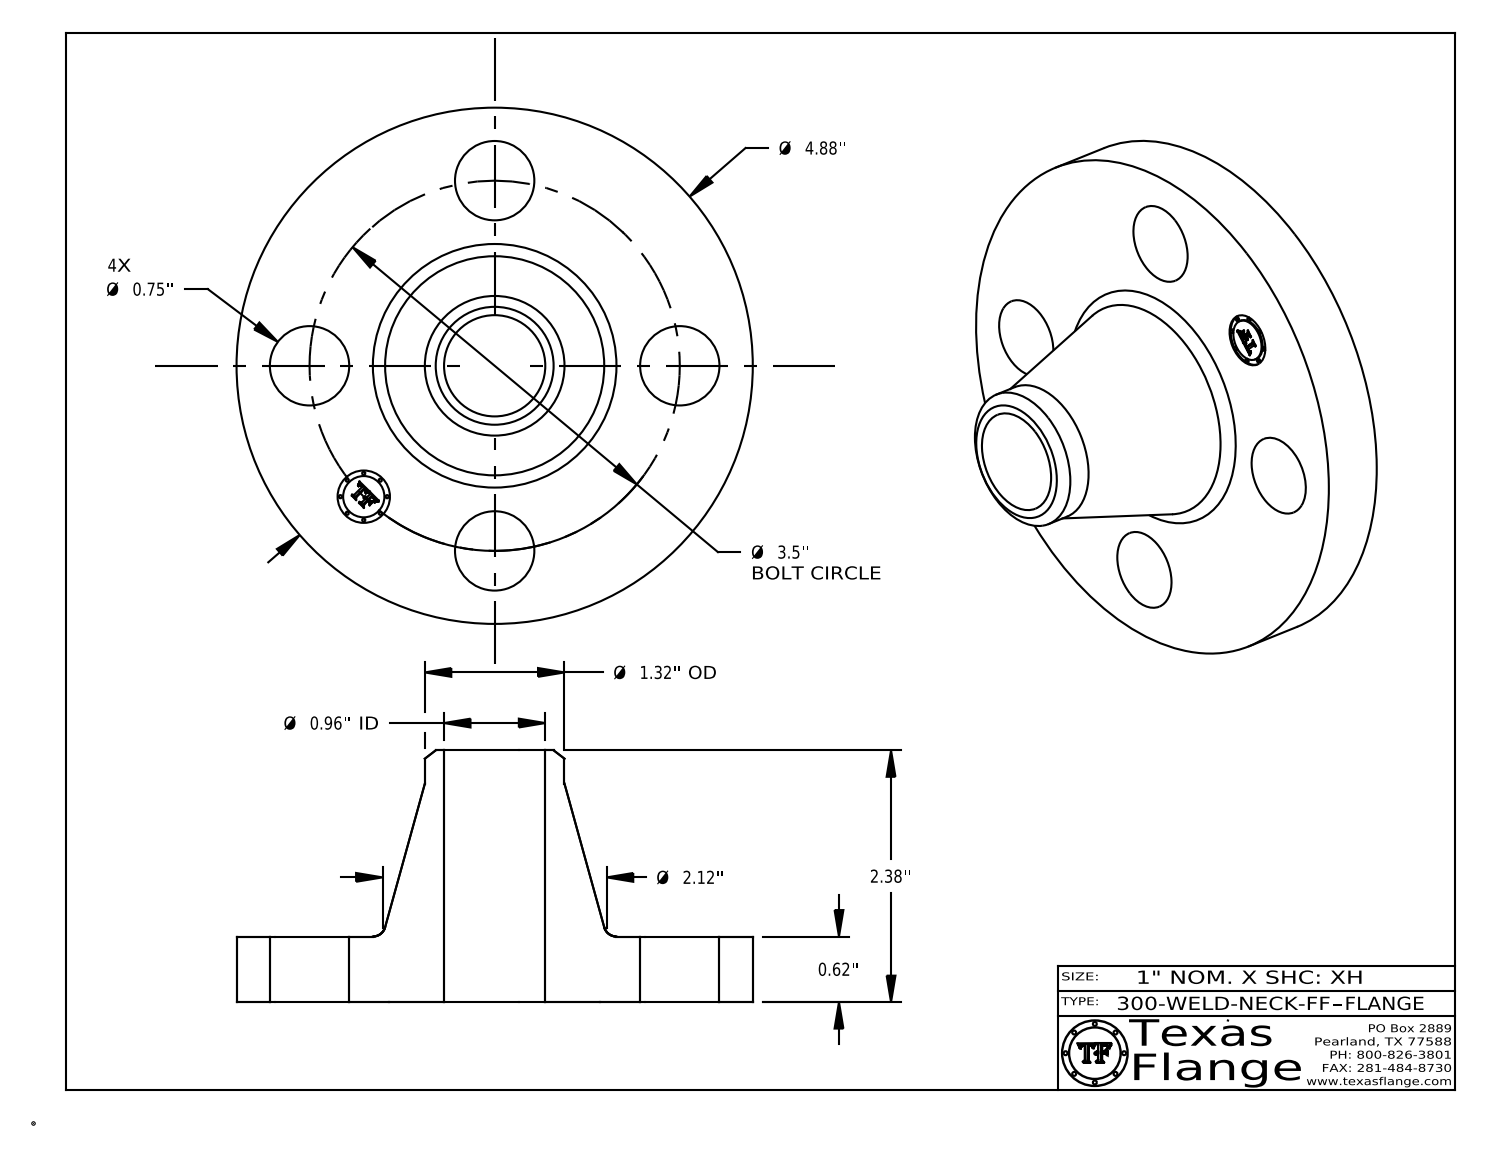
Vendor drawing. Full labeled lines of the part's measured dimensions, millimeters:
Part name (STEP PRODUCT): 300-WELD-NECK-FF
STEP written by: CATIA V5 STEP AP214 (AUTOMOTIVE_DESIGN)
Units: millimetres
Bodies: 1 solid, 409 faces (369 planar, 34 cylindrical, 6 other)
Overall size (bounding box): 124 × 124 × 60.5
Volume: 207 000 mm³ · Surface area: 39 920 mm²
Round holes (diameter × count): ⌀19.1 ×4, ⌀12.6 ×1, ⌀24.3 ×1
Round bosses / shafts (diameter × count): ⌀0.8 ×8, ⌀124 ×1, ⌀33.5 ×1, ⌀9.9 ×1
Main face-to-face distances: 15.7, 60.5, 44.7, 0.4, 15.4, 45.1, 3.8, 3.7, 0.7, 2.4
Hole centre spacings: 44.5, 62.9, 34, 82.1, 88.9
